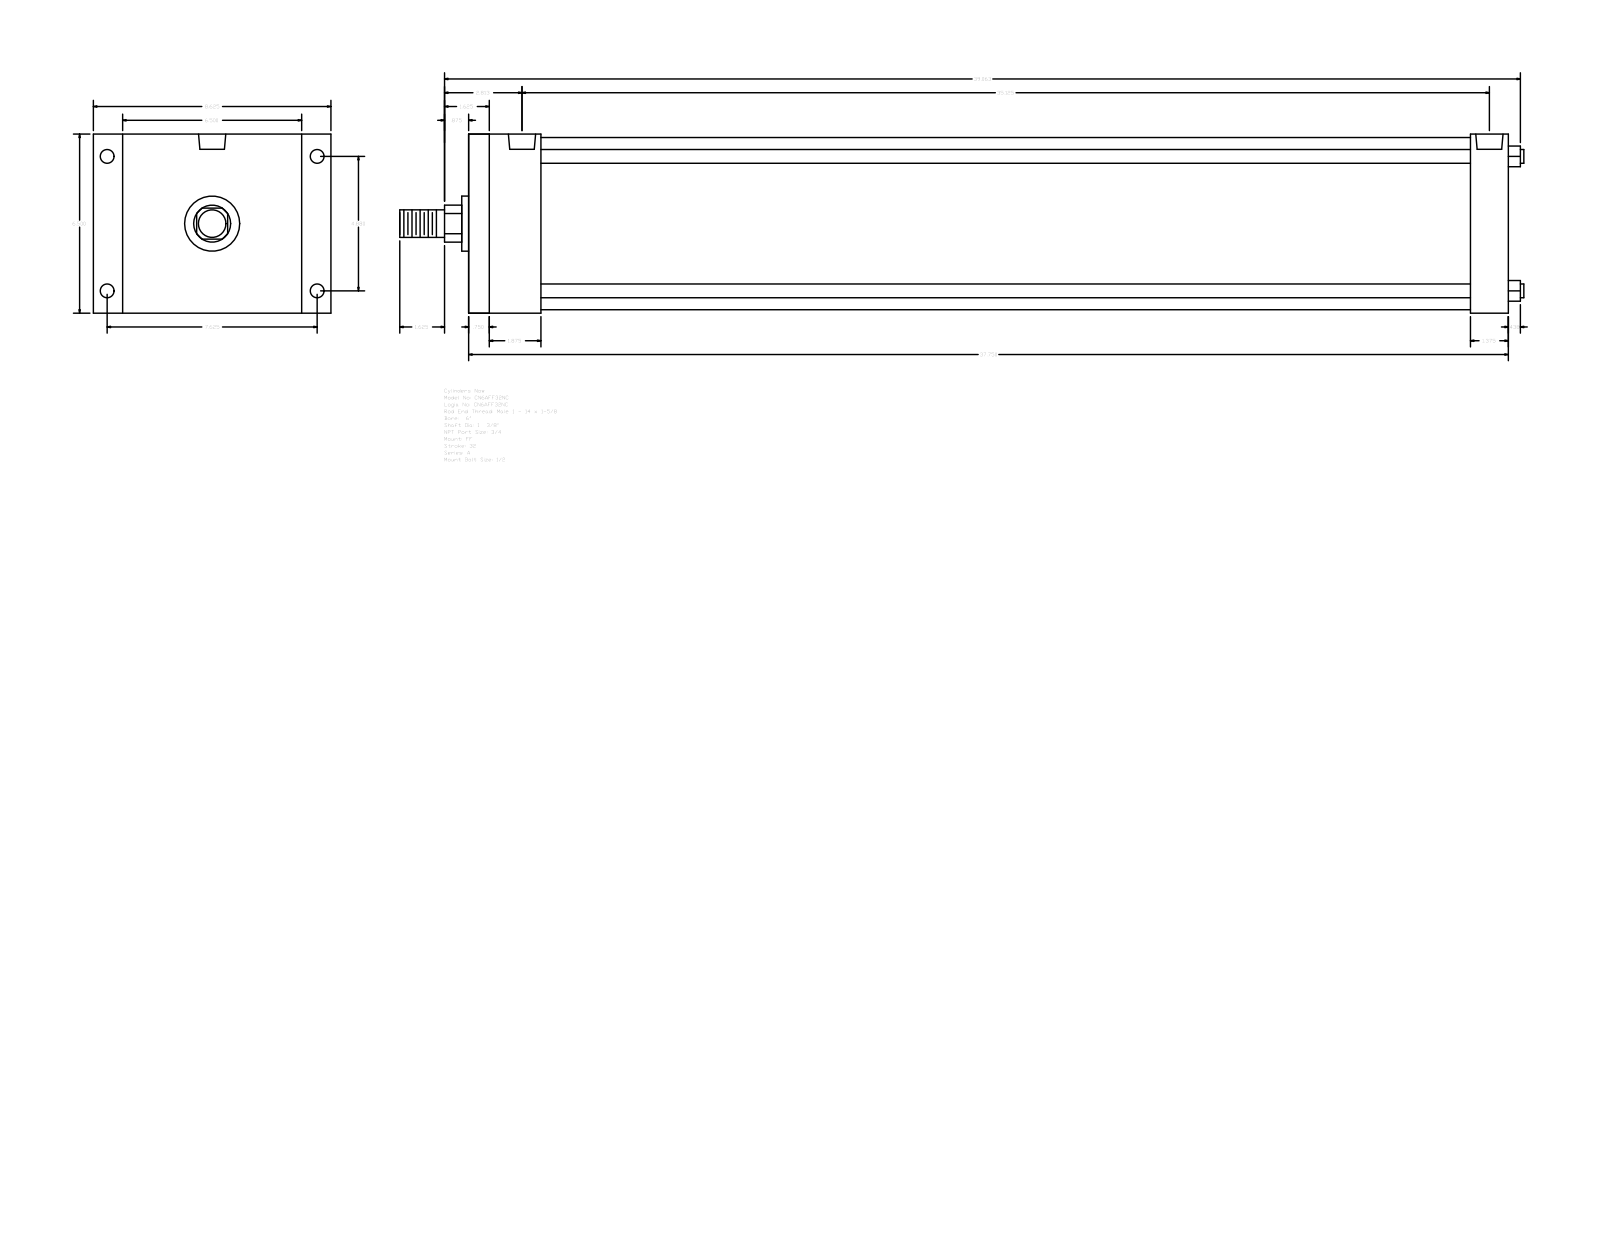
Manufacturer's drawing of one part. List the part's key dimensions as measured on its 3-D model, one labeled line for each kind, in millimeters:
Part name (STEP PRODUCT): A_FF__0600_1.375
STEP written by: GSSL Pune (CONFIG_CONTROL_DESIGN)
Units: millimetres
Bodies: 0 solids, 92 faces (64 planar, 28 cylindrical, 0 other)
Overall size (bounding box): 1036.64 × 219.07 × 165.1
Round holes (diameter × count): ⌀12.7 ×4, ⌀15.08 ×4, ⌀25.12 ×2
Round bosses / shafts (diameter × count): ⌀12.7 ×4, ⌀158.75 ×1, ⌀50.8 ×1, ⌀34.92 ×1, ⌀25.4 ×1
Partial cylindrical surfaces — rounded edges, fillets, slot ends (radius × count): R17.06 ×1
Main face-to-face distances: 165.1, 958.85, 19.04, 939.81, 66.67, 47.63, 892.18, 923.92, 904.88, 857.25
Hole centre spacings: 5.56, 123.96, 193.68, 229.95, 881.05, 886.61, 892.17
